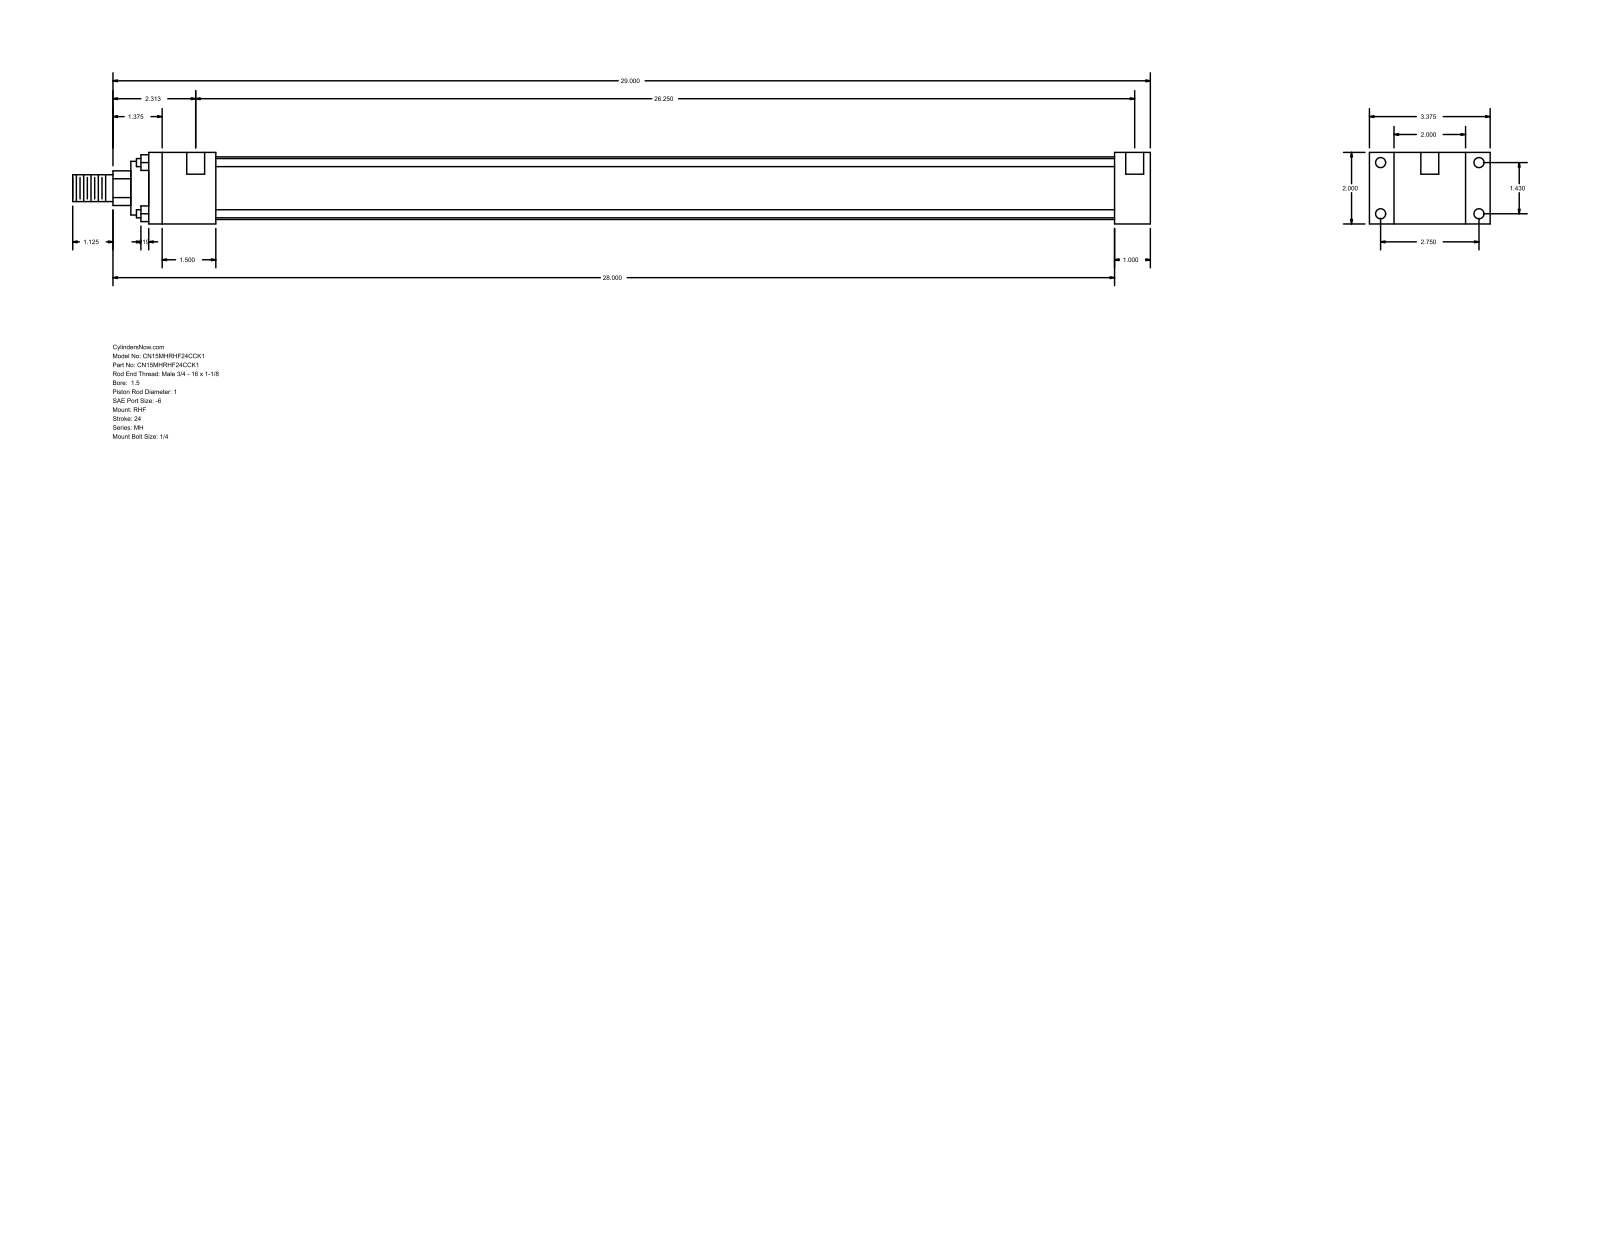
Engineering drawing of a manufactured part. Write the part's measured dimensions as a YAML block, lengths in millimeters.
part_name: "MH_RHF__0150_1"
step_written_by: "GSSL Pune (CONFIG_CONTROL_DESIGN)"
units: millimeters
bodies: {solids: 0, faces: 88, planar: 60, cylindrical: 28, other: 0}
overall_size: [765.17, 85.72, 50.8]
round_holes:
  - {diameter: 5.56, count: 4}
  - {diameter: 7.14, count: 4}
  - {diameter: 12.7, count: 2}
round_bosses_or_shafts:
  - {diameter: 5.71, count: 4}
  - {diameter: 44.45, count: 1}
  - {diameter: 38.1, count: 1}
  - {diameter: 25.4, count: 1}
  - {diameter: 19.05, count: 1}
partial_cylinders:
  - {radius: 12.29, count: 1}
face_to_face_distances: [50.8, 25.4, 17.46, 68.26, 85.72, 711.2, 685.8, 47.63, 638.17, 663.57]
hole_center_spacings: [36.32, 69.84, 78.72, 669.93, 3.18, 666.75]
